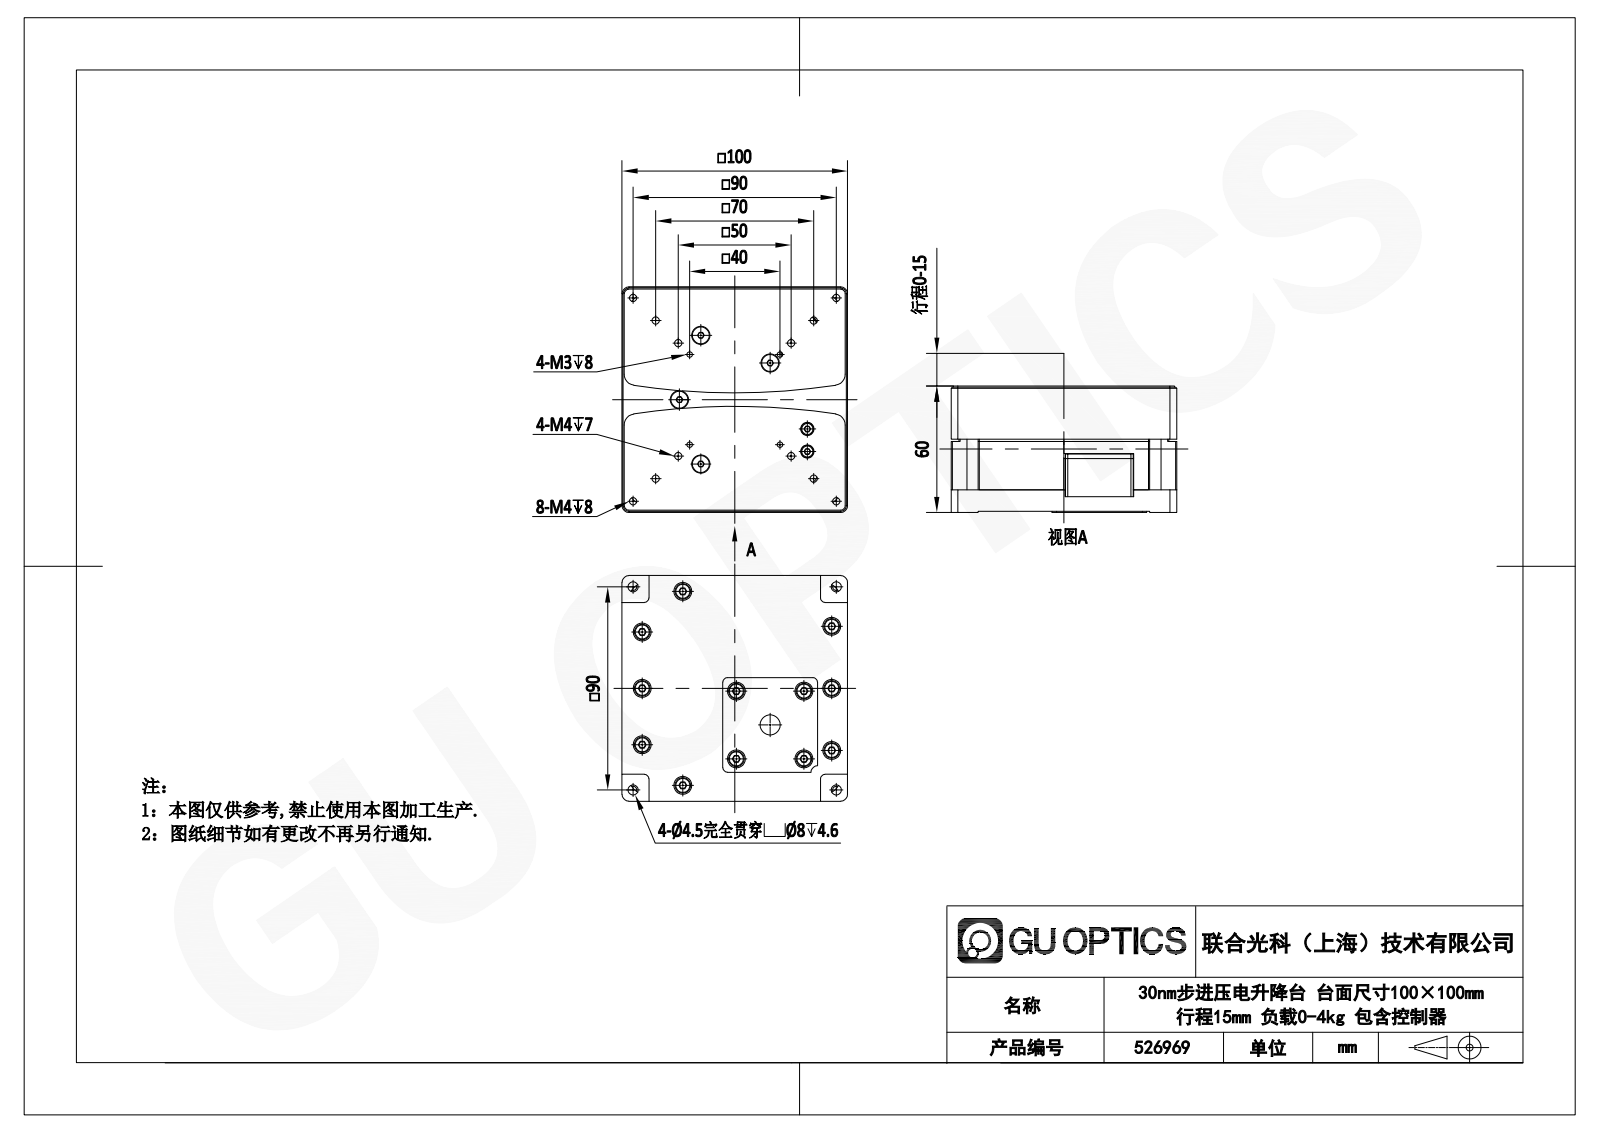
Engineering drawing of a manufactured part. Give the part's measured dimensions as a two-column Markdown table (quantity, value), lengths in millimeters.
| quantity | value |
| --- | --- |
| part name | 526969 |
| STEP written by | SolidWorks 2020 (CONFIG_CONTROL_DESIGN) |
| units | millimeters |
| bodies | 0 solids, 178 faces (88 planar, 82 cylindrical, 8 other) |
| overall size | 100 × 100 × 60 |
| round holes (diameter × count) | 3.3 × 12, 2.5 × 4, 4.5 × 4, 8 × 4, 8.2 × 4, 1.25 × 2, 3.1 × 2, 5.4 × 2, 6 × 2 |
| round bosses / shafts (diameter × count) | 8 × 3, 4.3 × 2, 2.5 × 2 |
| partial cylindrical surfaces (radius × count) | 5 × 8, 0.5 × 6, 2 × 4, 3 × 4, 1 × 2, 1.5 × 2, 300 × 2, 0.2 × 1 |
| main face-to-face distances | 100, 50, 3, 53, 12, 88, 49.5, 0.5, 27, 30 |
| hole center spacings | 14.14, 45.28, 57.01, 60.83, 69.64, 72.8, 80.62, 98.99 |
